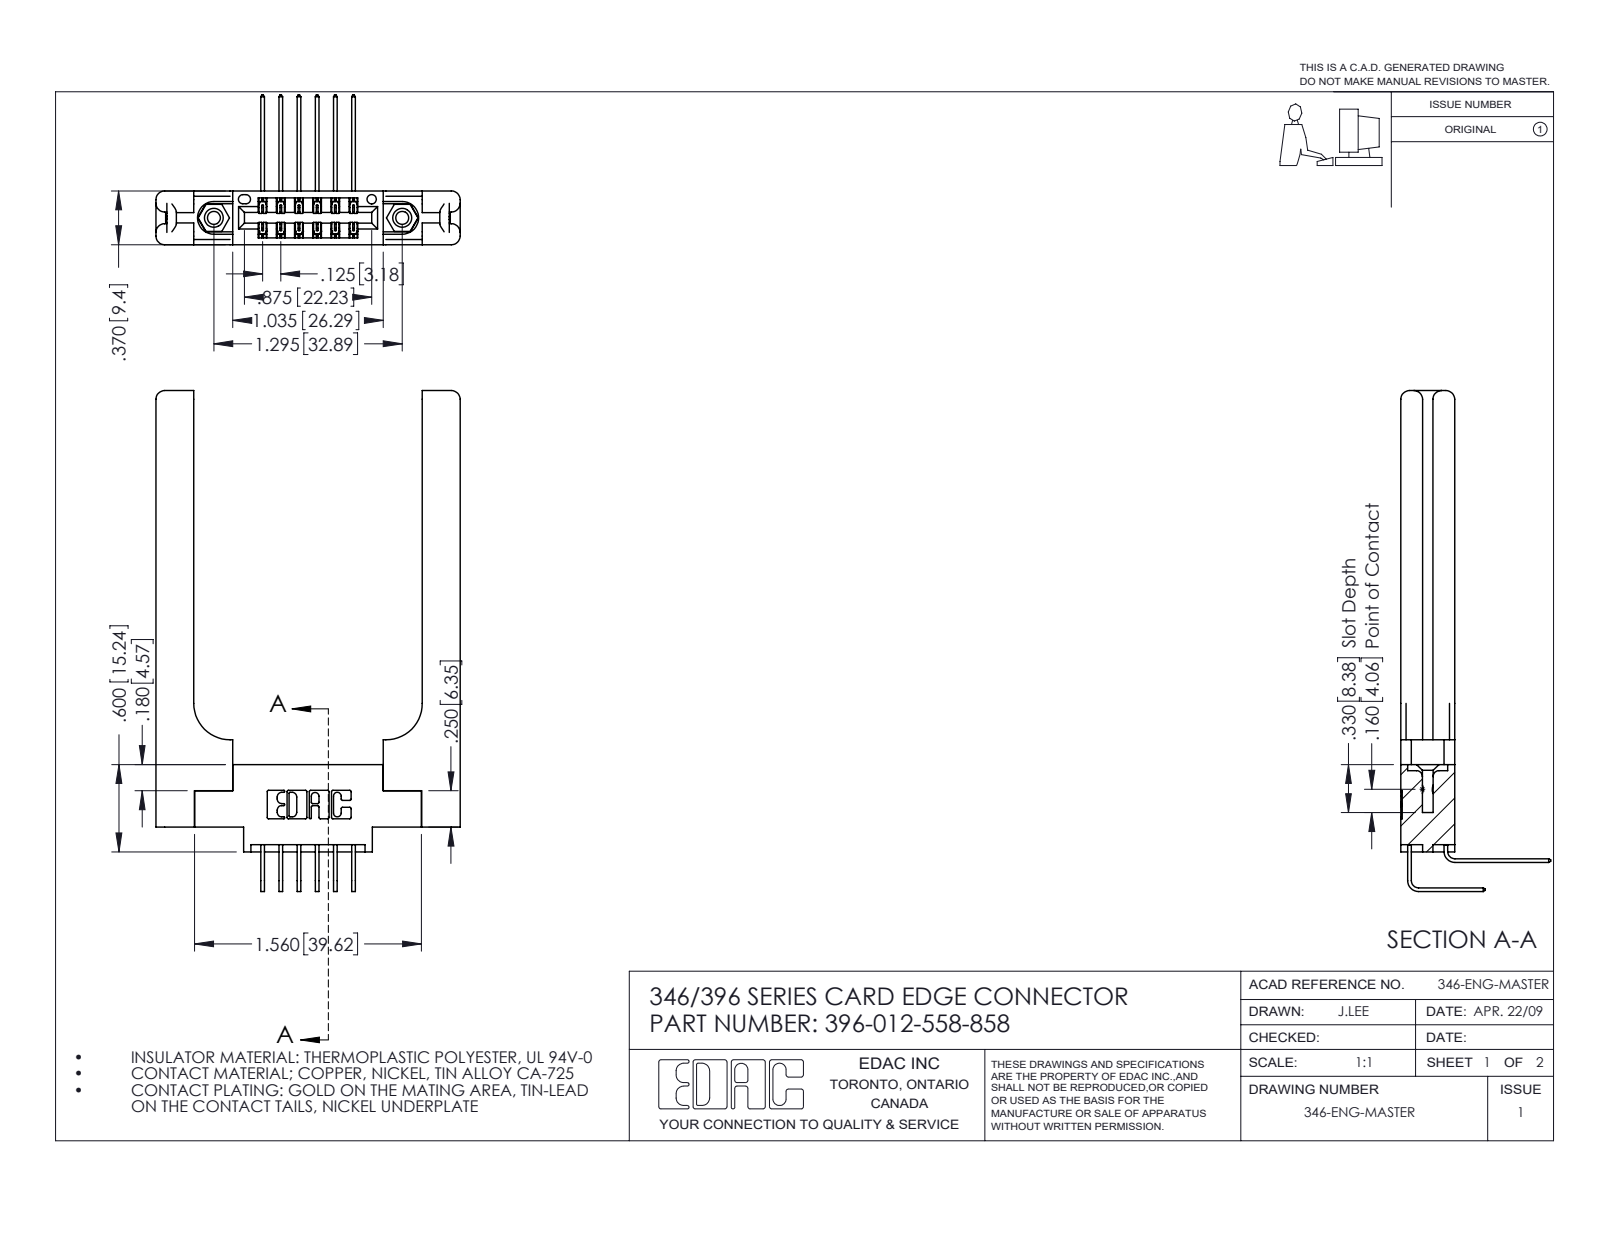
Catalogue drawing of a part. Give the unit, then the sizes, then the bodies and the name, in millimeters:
Units: millimetres
Overall size (bounding box): 87.5 × 53.1 × 26.2
Round holes (diameter × count): ⌀2.3 ×2, ⌀3.2 ×2, ⌀4 ×2, ⌀1.6 ×1
Round bosses / shafts (diameter × count): ⌀3.9 ×2
Partial cylindrical surfaces — rounded edges, fillets, slot ends (radius × count): R0.3 ×22, R0.2 ×18, R1.5 ×16, R0.2 ×6, R0.8 ×6, R0.7 ×3, R0.4 ×2, R0.6 ×2
Main face-to-face distances: 9.4, 3.8, 5.6, 1.8, 6.4, 3.8, 1.2, 39.9, 8.2, 0.6
Hole centre spacings: 6.2, 27.7, 32.9
Volume: 12 300 mm³ · Surface area: 11 540 mm²
Bodies: 17 solids, 1030 faces (672 planar, 298 cylindrical, 60 other)
Part name (STEP PRODUCT): 346-220-058_345-220-058; 345-292-001_558 Tail - 2; 345-250-001_345-250-001-102; 396-012-558-858 (+2 more)
STEP written by: SolidWorks 2016 (CONFIG_CONTROL_DESIGN)
